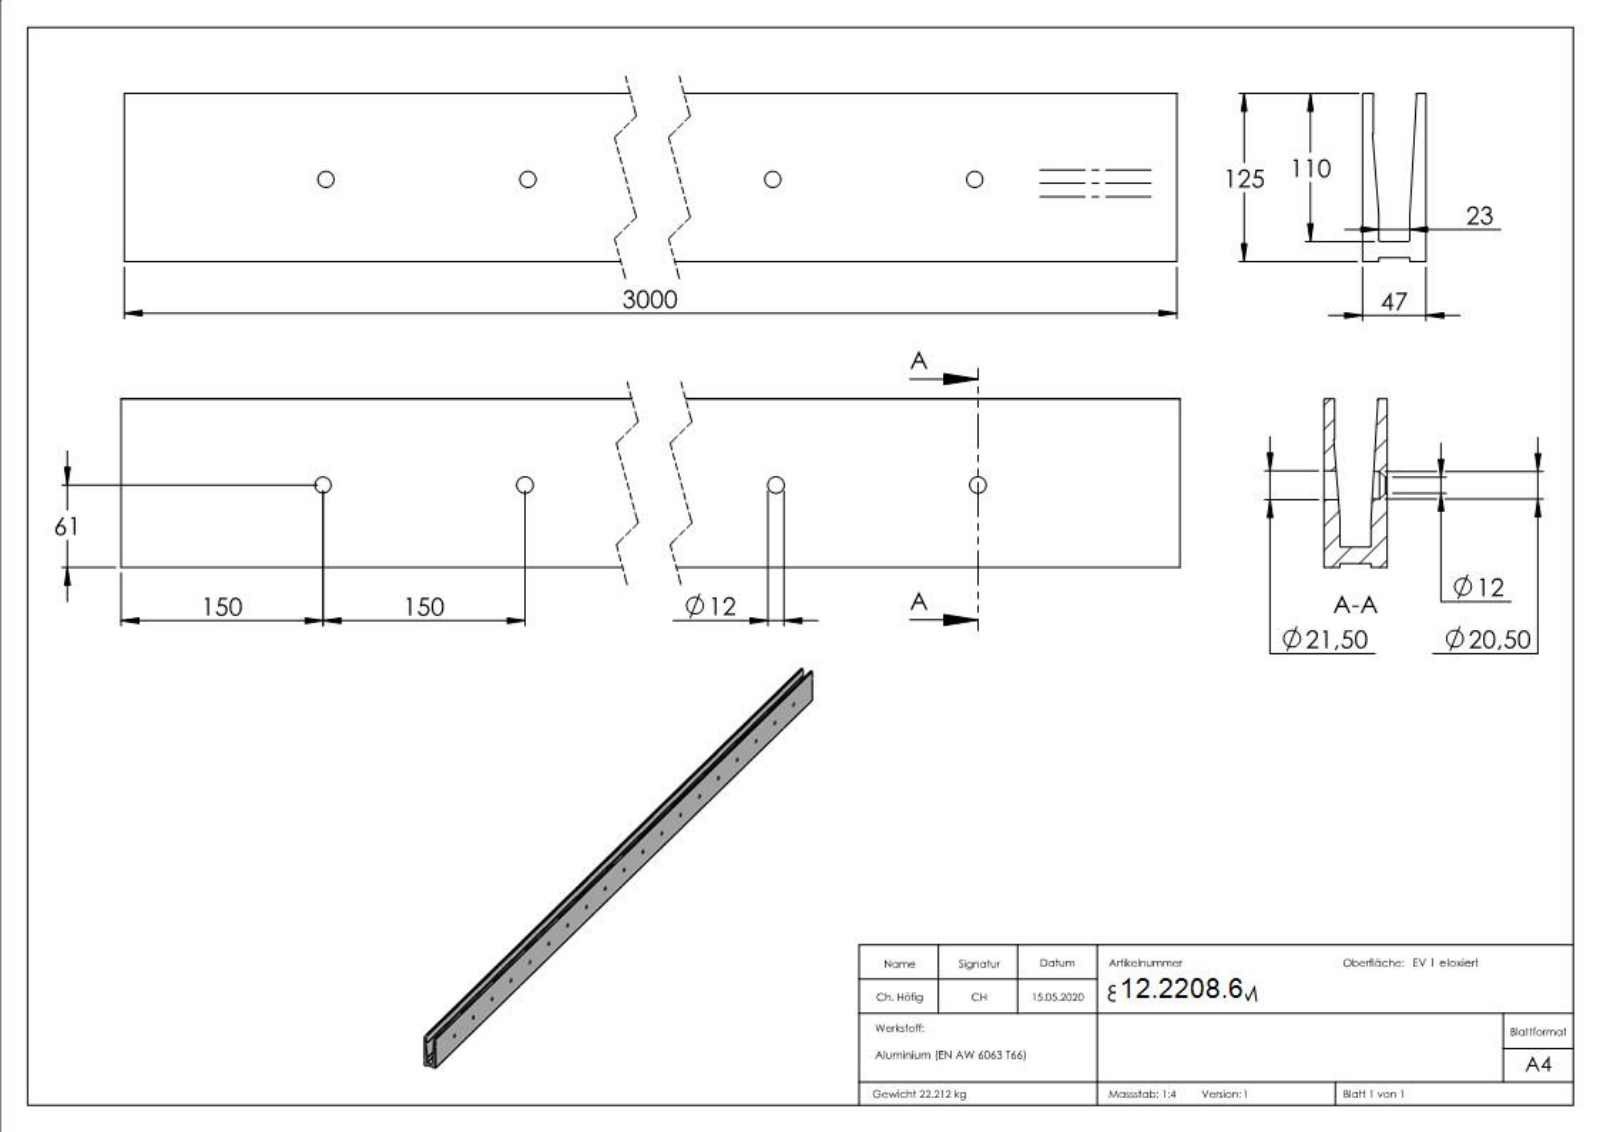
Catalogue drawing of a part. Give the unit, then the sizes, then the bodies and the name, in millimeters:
Units: millimetres
Overall size (bounding box): 3000 × 125 × 47
Round holes (diameter × count): ⌀12 ×19, ⌀20.5 ×19, ⌀21.5 ×19
Partial cylindrical surfaces — rounded edges, fillets, slot ends (radius × count): R0.5 ×4, R1 ×3, R0.65 ×2, R0.25 ×1
Main face-to-face distances: 47, 12, 35, 7.94, 39.06, 3, 4.06, 27.06, 23, 15
Hole centre spacings: 150, 300, 450, 600, 750, 900, 1050, 1200
Volume: 8 227 000 mm³ · Surface area: 1 688 000 mm²
Bodies: 1 solid, 437 faces (152 planar, 125 cylindrical, 160 other)
Part name (STEP PRODUCT): 80600-ALU-3M
STEP written by: SolidWorks 2015 (CONFIG_CONTROL_DESIGN)
